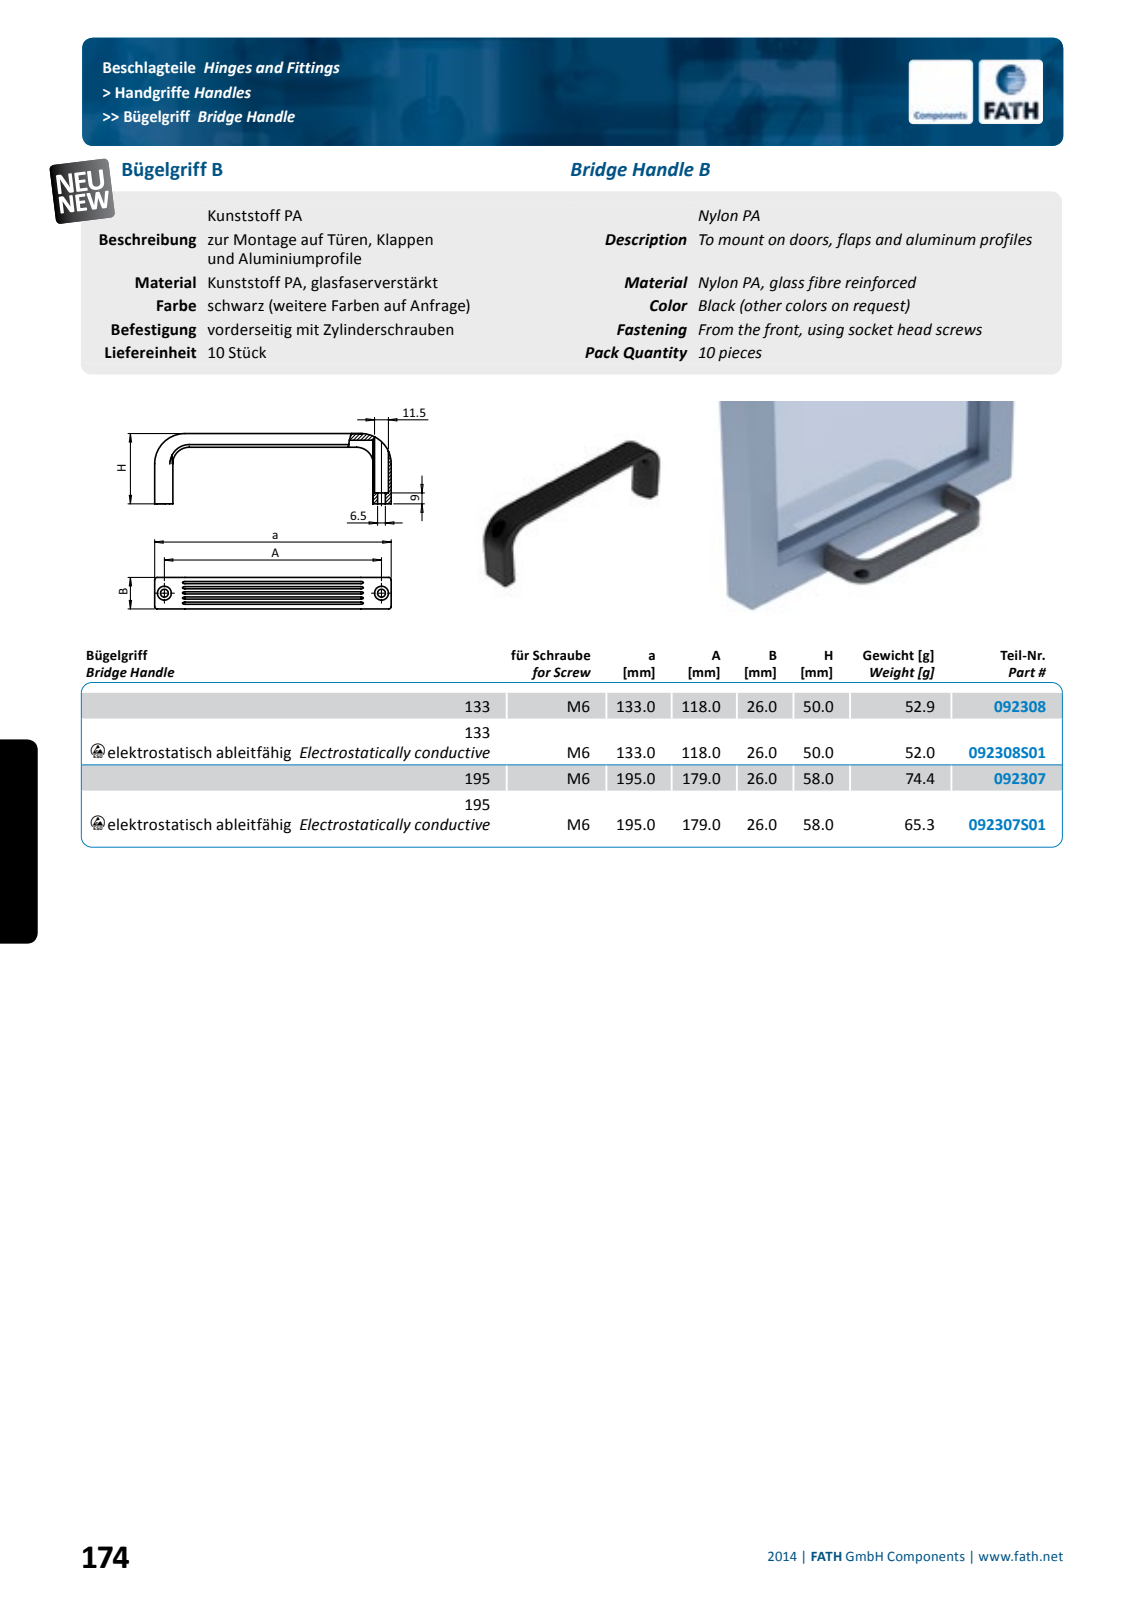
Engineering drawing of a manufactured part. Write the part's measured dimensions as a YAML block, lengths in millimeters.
part_name: "fath_092307s01"
step_written_by: "Spatial InterOp 3D (automotive_design)"
units: millimeters
bodies: {solids: 1, faces: 333, planar: 159, cylindrical: 96, other: 78}
overall_size: [195, 58, 26]
volume: 55060
surface_area: 31024
round_holes:
  - {diameter: 6.5, count: 2}
  - {diameter: 11.5, count: 2}
  - {diameter: 5, count: 1}
partial_cylinders:
  - {radius: 0.5, count: 12}
  - {radius: 1, count: 8}
  - {radius: 2, count: 6}
  - {radius: 4, count: 6}
  - {radius: 1.5, count: 5}
  - {radius: 23.12, count: 3}
  - {radius: 1.2, count: 2}
  - {radius: 7.25, count: 2}
face_to_face_distances: [6.9, 5.5, 3.7, 7.95, 18.05, 11.15, 14.85, 3.2, 2, 26]
hole_center_spacings: [24.5, 154.5, 179]
